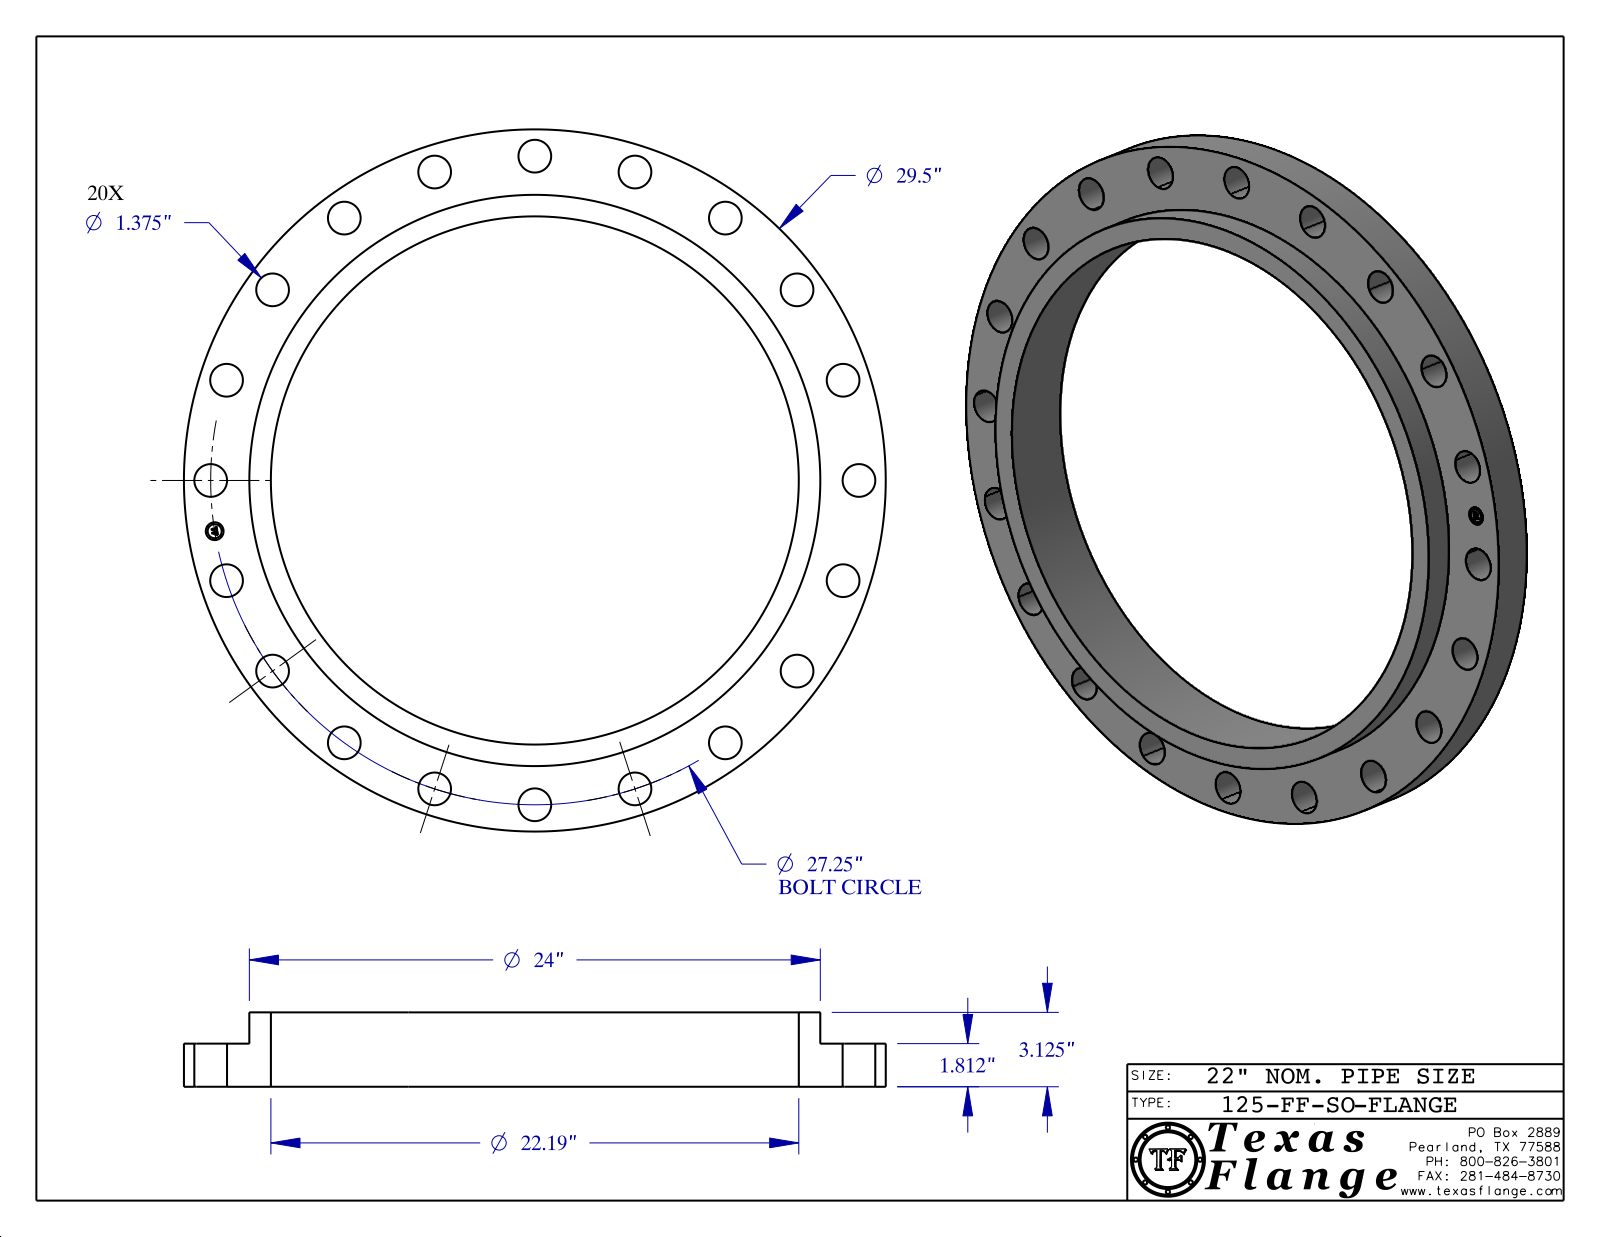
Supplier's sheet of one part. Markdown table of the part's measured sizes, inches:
| quantity | value |
| --- | --- |
| part name | 125-FF-SO-B16.1 |
| STEP written by | CATIA V5 STEP AP214 (AUTOMOTIVE_DESIGN) |
| units | inches |
| bodies | 1 solid, 434 faces (368 planar, 66 cylindrical, 0 other) |
| overall size | 29.5 × 29.5 × 3.125 |
| volume | 570.1 in³ |
| surface area | 1 176 in² |
| round holes (diameter × count) | 1.375 × 20, 0.75 × 1, 22.19 × 1 |
| round bosses / shafts (diameter × count) | 0.045 × 8, 29.5 × 1, 24 × 1, 0.591 × 1 |
| main face-to-face distances | 1.812, 3.125, 1.313, 1.797, 0.015, 1.328, 0.014, 0.224, 0.219, 0.041 |
| hole center spacings | 13.625, 19.269, 25.917, 8.421, 12.371, 4.263, 16.017, 22.046 |
